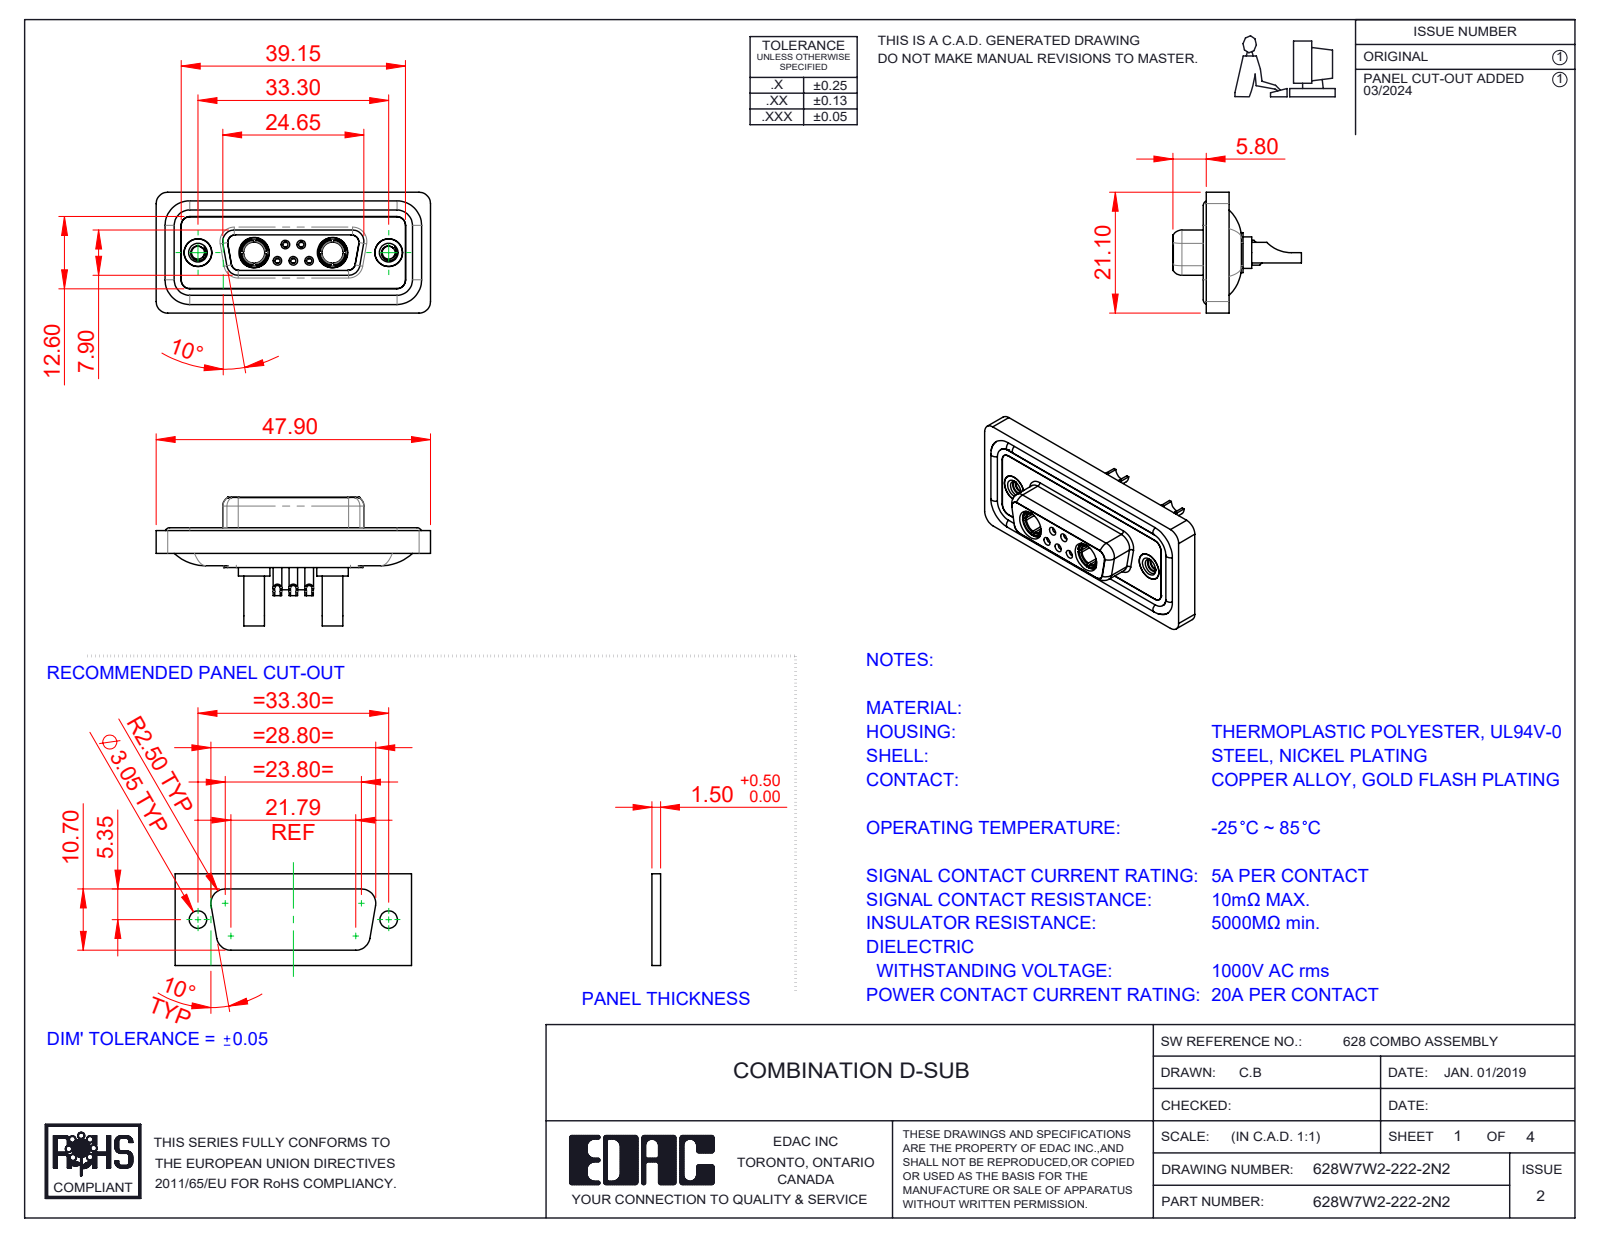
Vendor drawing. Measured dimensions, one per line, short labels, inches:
name: 628W7W2-222-2N2; 628Combo Housing_7W2; 628Combo Shell Front_15 Contacts; 628Combo Threaded Rivet_2 (+5 more)
written by: SolidWorks 2023 (CONFIG_CONTROL_DESIGN)
unit: in
bodies: 16 solids, 821 faces (254 planar, 345 cylindrical, 222 other)
size: 1.886 × 0.884 × 0.831
volume: 0.373 in³; area: 15.66 in²
holes: 5× ⌀0.035, 5× ⌀0.039, 5× ⌀0.043, 5× ⌀0.059, 5× ⌀0.079, 4× ⌀0.191, 3× ⌀0.063, 2× ⌀0.067, 2× ⌀0.089, 2× ⌀0.106, 2× ⌀0.146, 2× ⌀0.157
bosses: 6× ⌀0.063, 5× ⌀0.087, 2× ⌀0.217, 2× ⌀0.205, 2× ⌀0.195, 2× ⌀0.195, 2× ⌀0.189, 2× ⌀0.187
rounds: 22× R0.059, 20× R0.079, 12× R0.053, 8× R0.063, 6× R0.039, 4× R0.01, 4× R0.02, 4× R0.024
face distances: 0.016, 0.071, 0.063, 0.02, 0.114, 0.043, 0.293, 0.222, 0.26, 0.278
hole spacings: 0.124, 0.109, 0.386, 0.925, 0.17, 0.17, 0.198, 0.198
